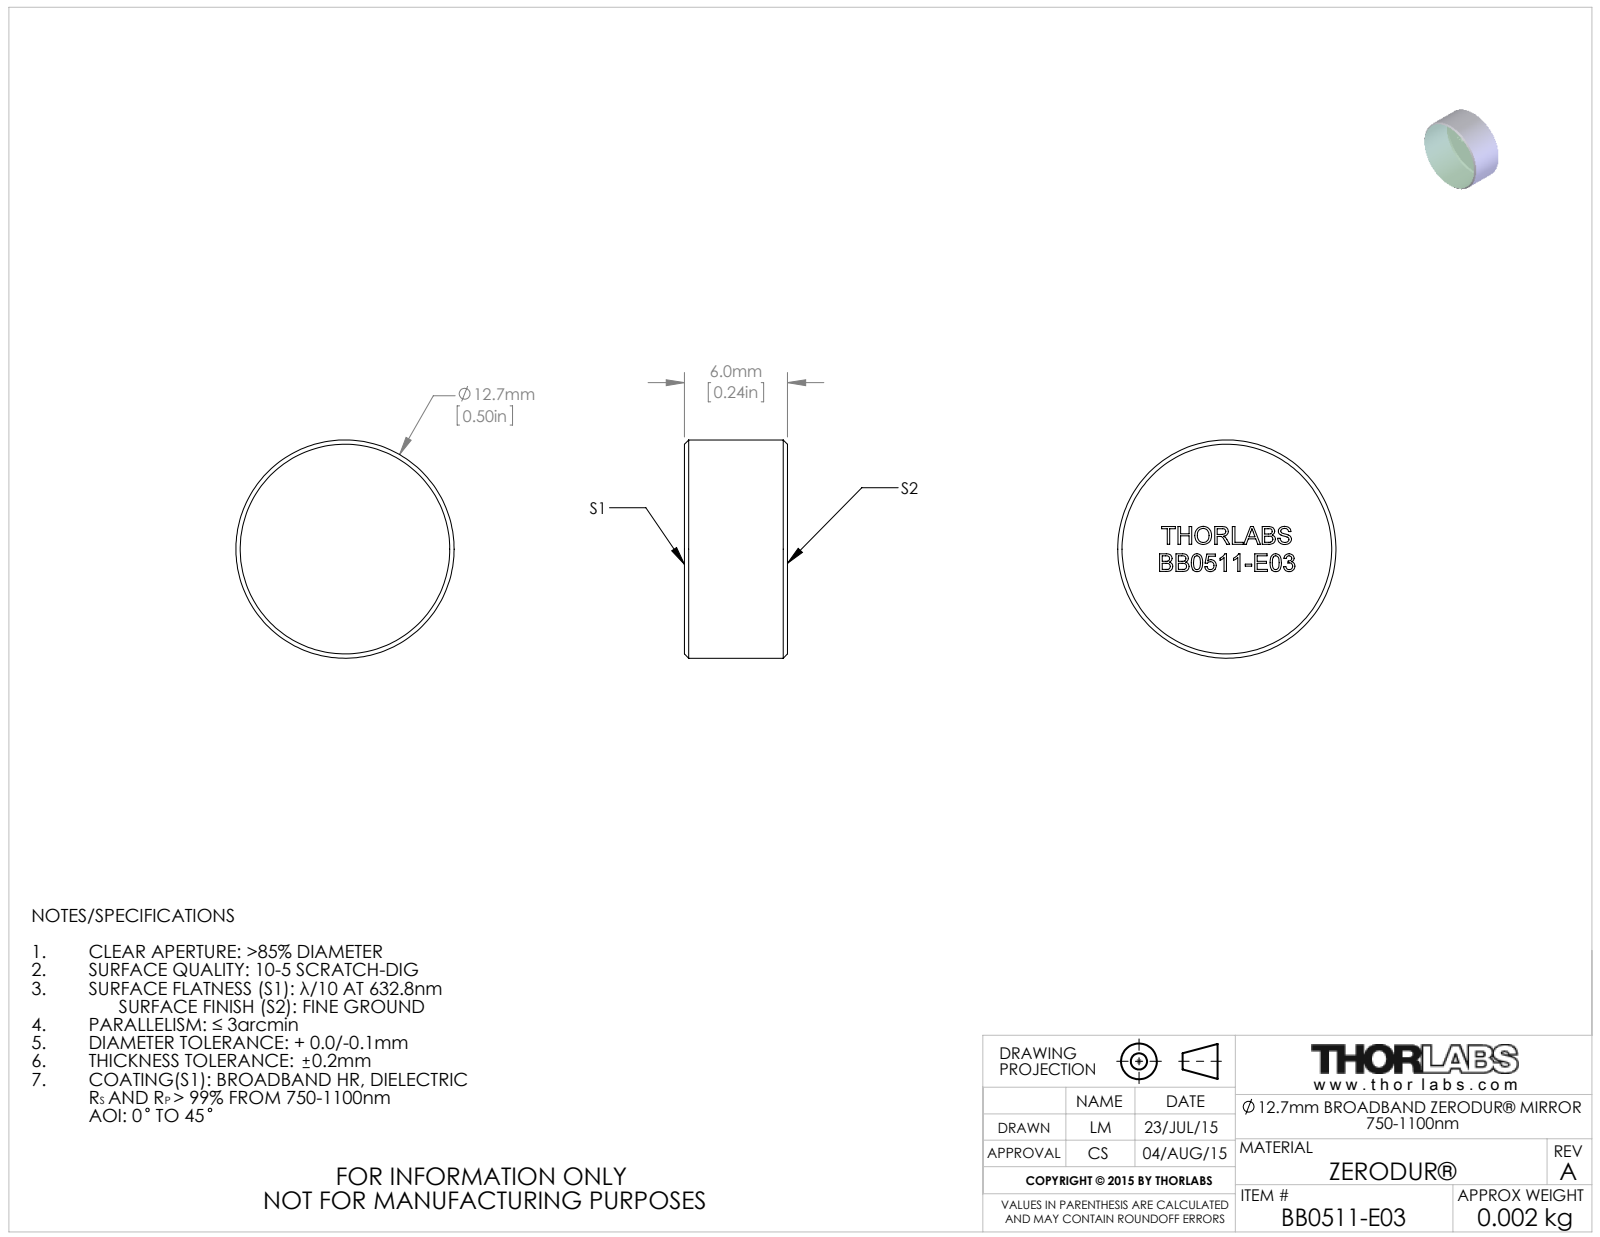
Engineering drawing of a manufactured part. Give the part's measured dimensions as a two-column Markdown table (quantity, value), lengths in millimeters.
| quantity | value |
| --- | --- |
| part name | TTN045134-E0W |
| STEP written by | SolidWorks 2014 (CONFIG_CONTROL_DESIGN) |
| units | millimeters |
| bodies | 1 solid, 259 faces (144 planar, 2 cylindrical, 113 other) |
| overall size | 12.7 × 12.7 × 6 |
| volume | 758 mm³ |
| surface area | 481 mm² |
| round bosses / shafts (diameter × count) | 12.7 × 1 |
| main face-to-face distances | 6, 1.58, 0.44, 0.79, 0.91, 1.03, 1.46, 1.28, 2.02, 0.67 |
